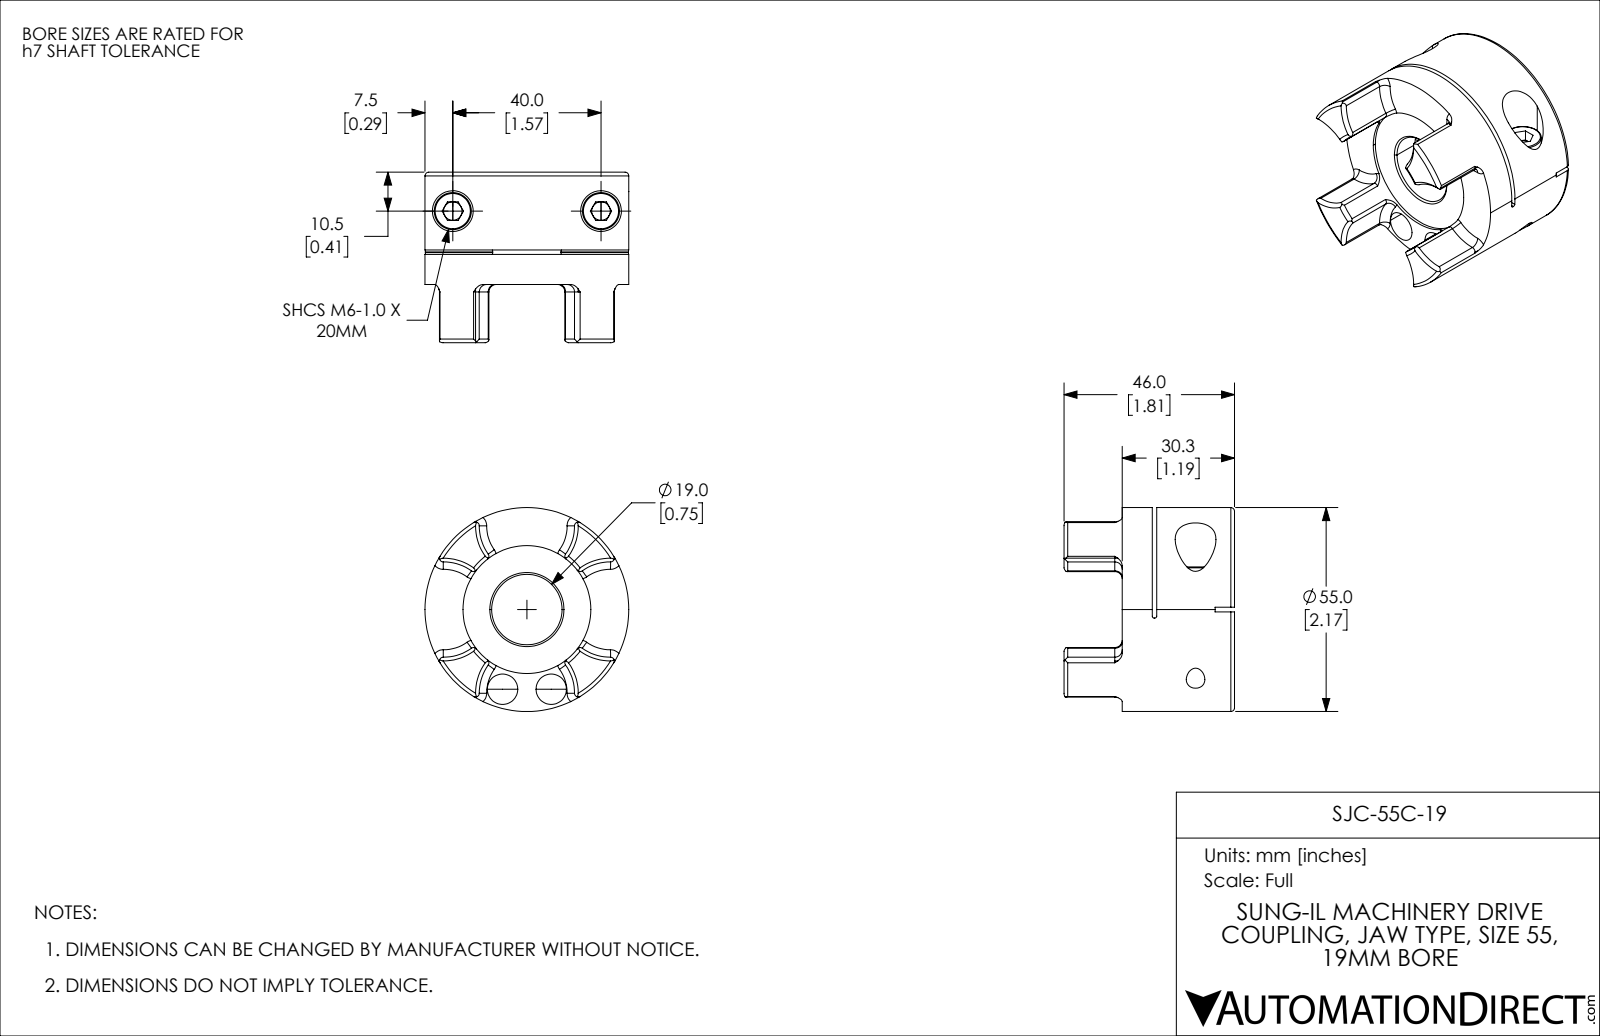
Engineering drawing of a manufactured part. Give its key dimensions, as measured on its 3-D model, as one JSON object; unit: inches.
{"part_name": "SJC-55C-19", "step_written_by": "SolidWorks 2021 (CONFIG_CONTROL_DESIGN)", "units": "inches", "bodies": {"solids": 3, "faces": 206, "planar": 52, "cylindrical": 72, "other": 82}, "overall_size": [2.165, 2.165, 1.811], "volume_in3": 3.912, "surface_area_in2": 31.37, "round_holes": [[0.197, 2], [0.252, 2], [0.323, 2], [0.433, 2], [0.748, 1], [1.358, 1]], "round_bosses_or_shafts": [[0.394, 2], [0.236, 2], [2.165, 1]], "partial_cylinders_radius": [[0.039, 16], [0.506, 4], [0.02, 2], [1.969, 1]], "face_to_face_distances": [0.874, 0.047, 0.827, 0.319, 0.366, 1.193, 0.031, 0.287, 0.335, 1.161], "hole_center_spacings": [0.885, 0.517, 1.575]}
